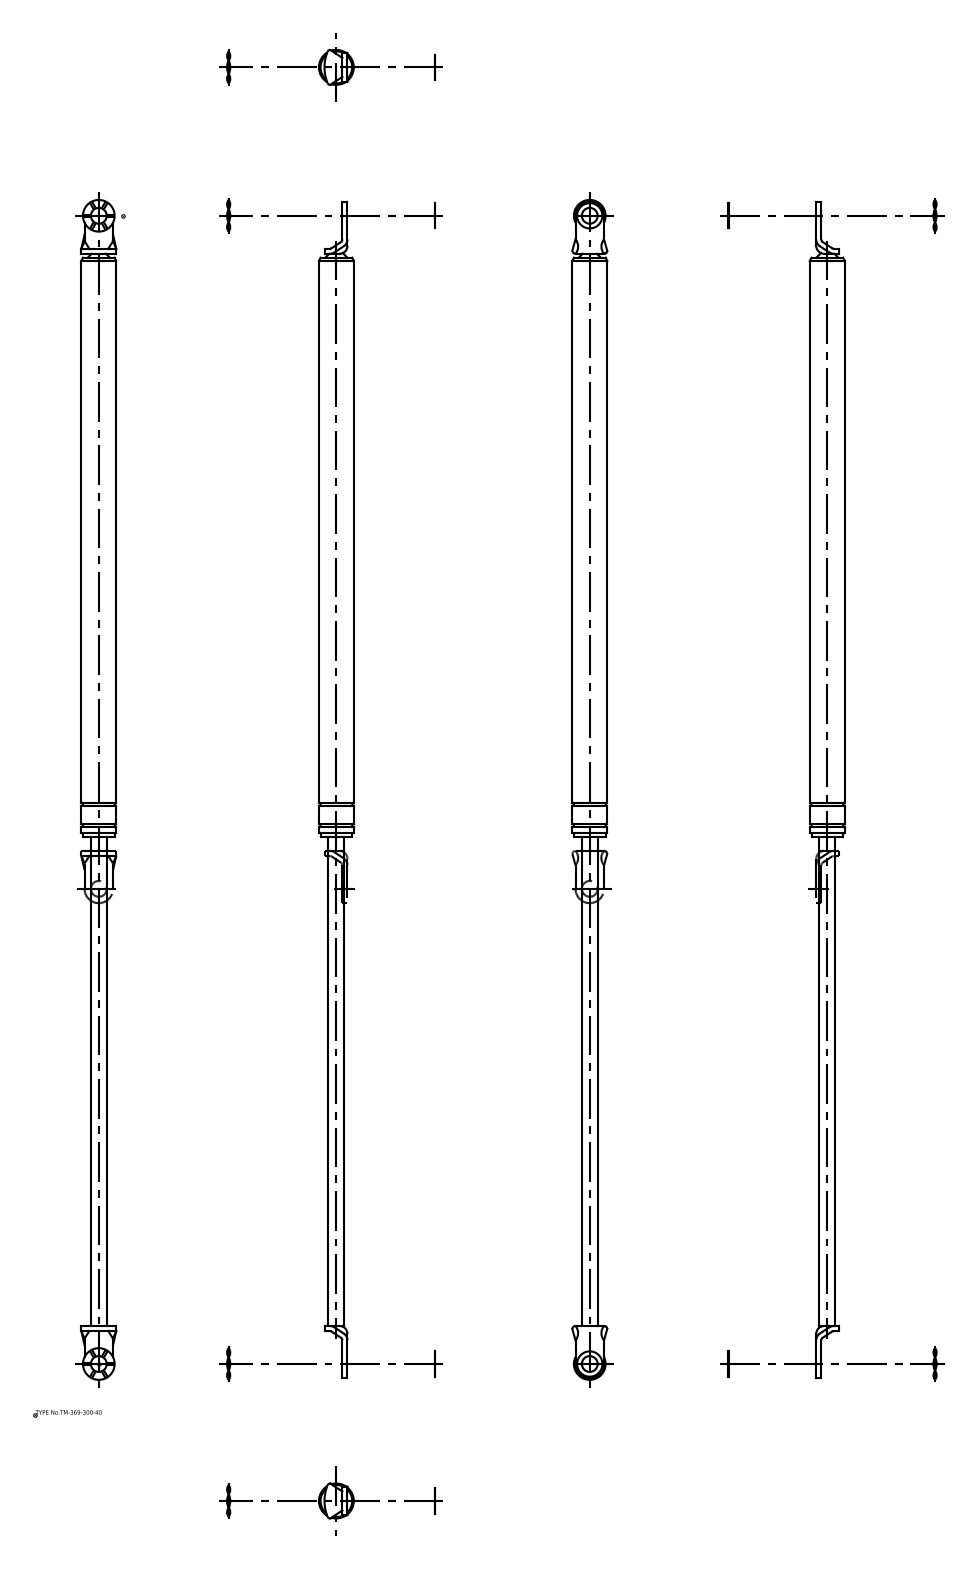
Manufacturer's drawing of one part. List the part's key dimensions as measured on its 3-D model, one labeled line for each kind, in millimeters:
Part name (STEP PRODUCT): ウェーブワッシャー; ワッシャー; 本体; 本体_div
STEP written by: spGate 16.7.1 (AUTOMOTIVE_DESIGN)
Units: millimetres
Bodies: 6 solids, 95 faces (43 planar, 44 cylindrical, 8 other)
Overall size (bounding box): 745 × 22.5 × 22.5
Volume: 168 912 mm³ · Surface area: 41 425 mm²
Round holes (diameter × count): ⌀10 ×2
Round bosses / shafts (diameter × count): ⌀20 ×3, ⌀16 ×2, ⌀22.5 ×1, ⌀22 ×1, ⌀10 ×1
Partial cylindrical surfaces — rounded edges, fillets, slot ends (radius × count): R4.4 ×2, R5 ×2, R9 ×2, R26.32 ×1
Main face-to-face distances: 3.2, 2, 5.2, 5.7, 680.2, 3.7, 0.5, 371.2, 312.2, 683.4
Hole centre spacings: 725
